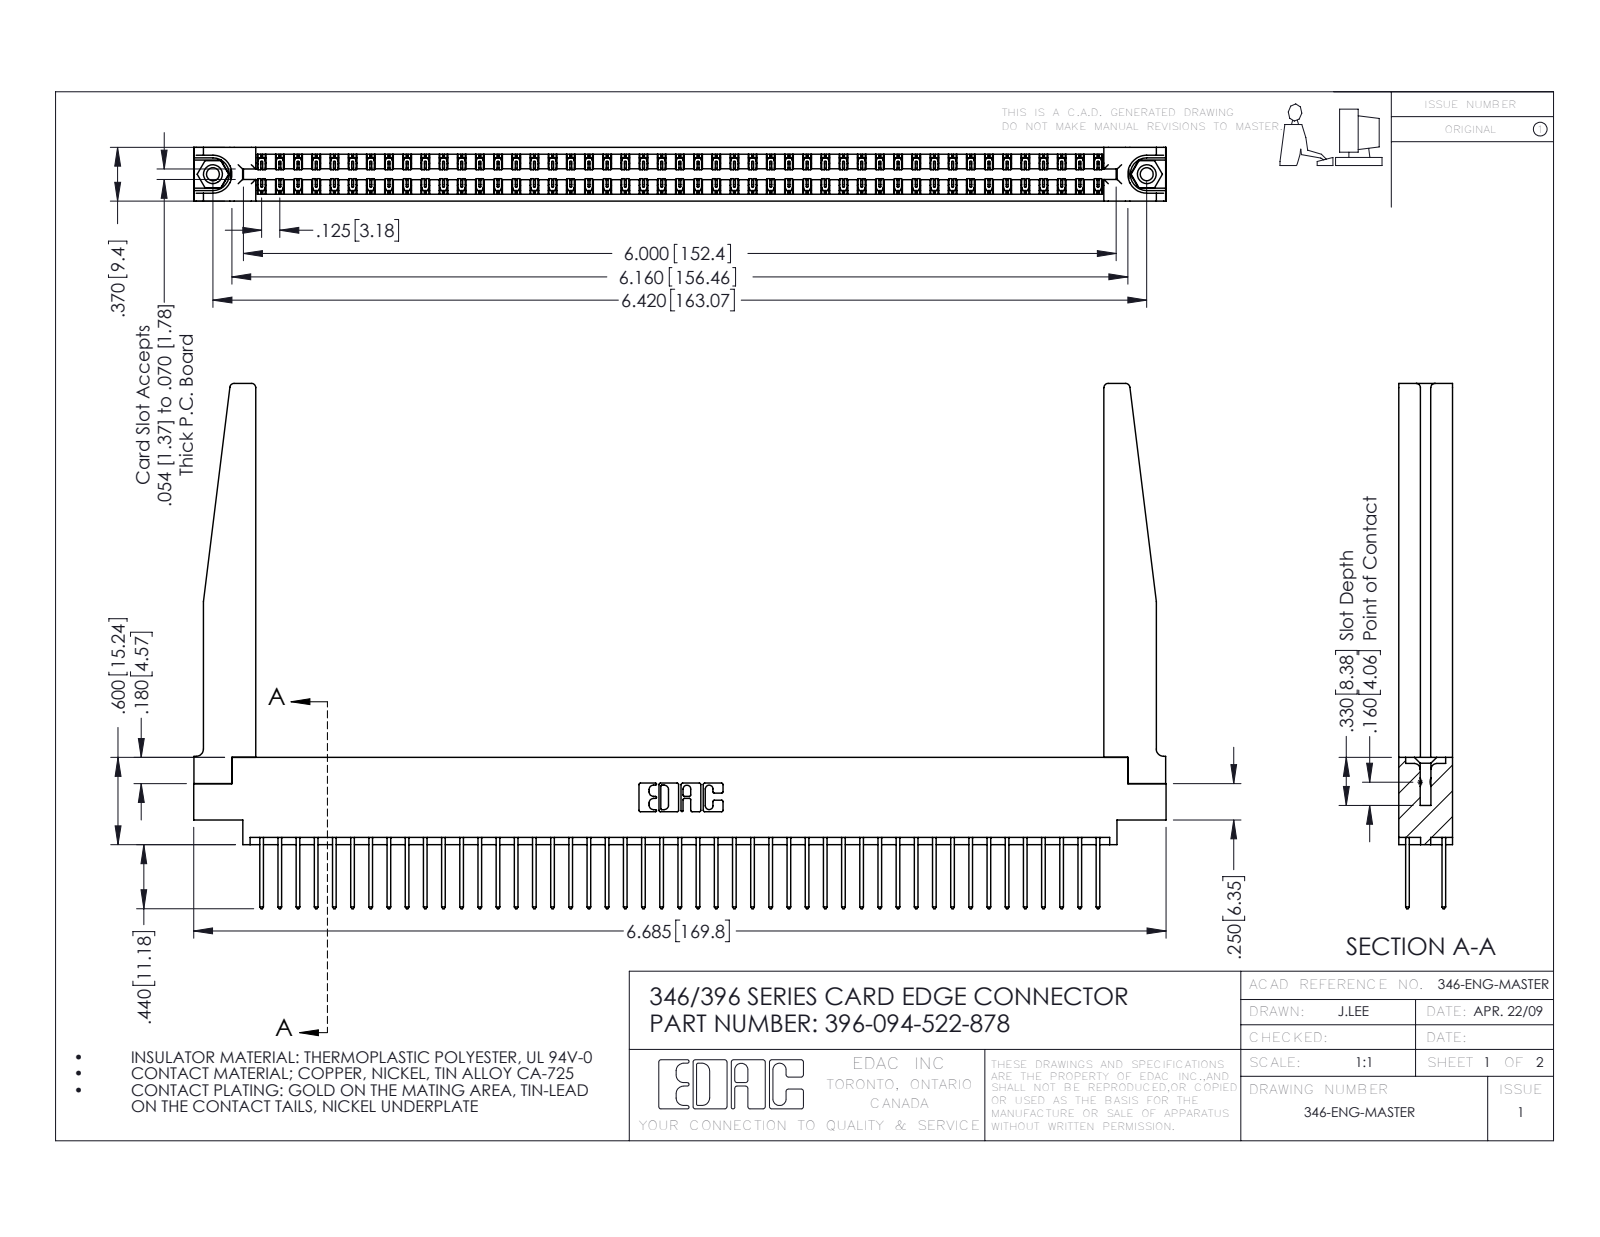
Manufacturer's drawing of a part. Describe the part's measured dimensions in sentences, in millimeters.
The part is named "345-292-001_345-293-122; 346 Part_0.170 Offset - 0.156 Dia-TH; 396-094-522-878; 346-220-078_345-220-078 (+1 more)". Its 3-D file was written by "SolidWorks 2016 (CONFIG_CONTROL_DESIGN)". It is 99 solids with 5248 faces: 3512 planar, 1684 cylindrical and 52 other. Overall it measures 169.8 by 91.7 by 9.4 millimeters. Its volume is 23 600 cubic millimeters and its surface area 30 850 square millimeters. Round holes: 2 of diameter 2.3, 2 of diameter 3.2, 2 of diameter 4, 1 of diameter 1.6. Round bosses or shafts: 2 of diameter 3.9. Partial cylindrical surfaces (rounded edges, fillets, slot ends): 141 of radius 0.2, 94 of radius 0.3, 22 of radius 0.3, 8 of radius 0.8, 6 of radius 0.2, 6 of radius 0.8, 3 of radius 0.7, 2 of radius 0.4. The main face-to-face distances are 1.2, 8.2, 9.4, 1.8, 6.4, 7.6, 0.6, 3.8, 3.8, 7. The hole center spacings are 6.2, 157.8, 163.1.
